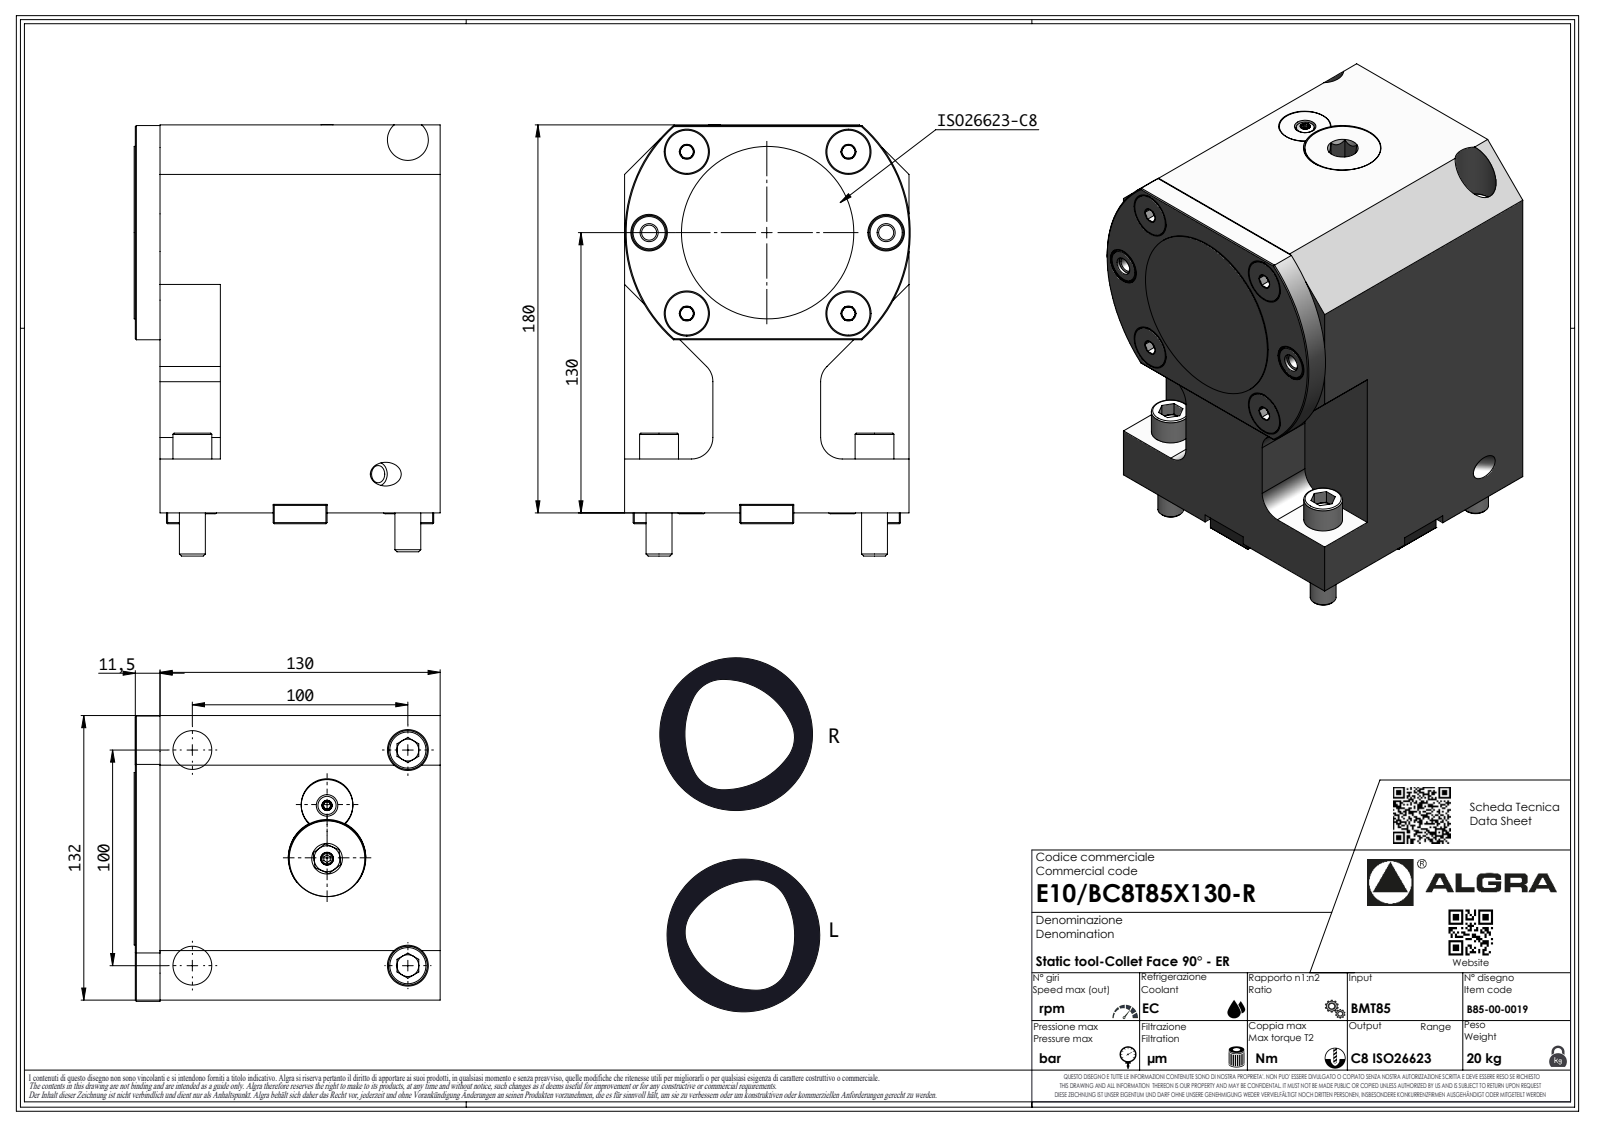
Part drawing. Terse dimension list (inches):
name: E10BC8T85X130-R
written by: SolidWorks 2023 (AUTOMOTIVE_DESIGN)
unit: in
bodies: 1 solid, 437 faces (288 planar, 39 cylindrical, 110 other)
size: 7.874 × 5.591 × 5.219
volume: 185.7 in³; area: 213.3 in²
holes: 1× ⌀0.083
bosses: 4× ⌀0.472, 2× ⌀0.709, 1× ⌀3.15, 1× ⌀0.251, 1× ⌀0.067
rounds: 7× R0.013, 7× R0.02, 7× R0.146, 4× R0.394, 1× R0.008, 1× R2.605
face distances: 5.197, 7.087, 5.118, 5.571, 0.453, 0.472, 0.02, 5.591, 4.016, 1.102
